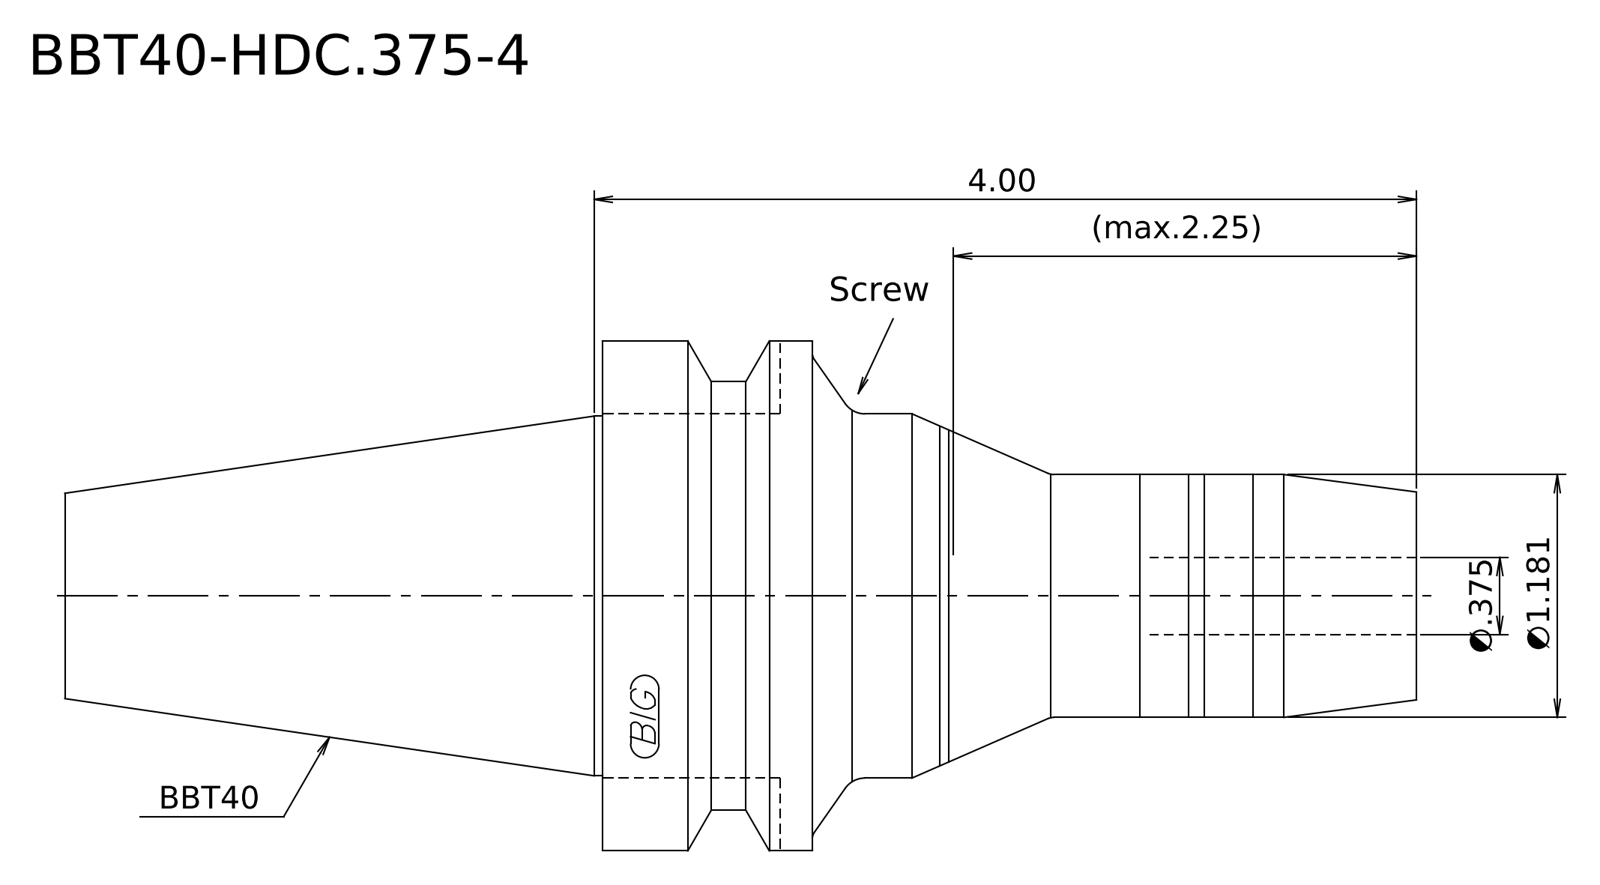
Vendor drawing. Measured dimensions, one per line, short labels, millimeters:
written by: Kubotek KeyCreator 2011 V10.0.2 (22737) (automotive_design)
unit: mm
bodies: 1 solid, 16 faces (4 planar, 6 cylindrical, 6 other)
size: 167 × 63 × 63
volume: 212 879 mm³; area: 25 067 mm²
bosses: 1× ⌀63, 1× ⌀53, 1× ⌀45, 1× ⌀44.45, 1× ⌀30
face distances: 100.6, 167, 66.4, 74.6, 26, 92.4
